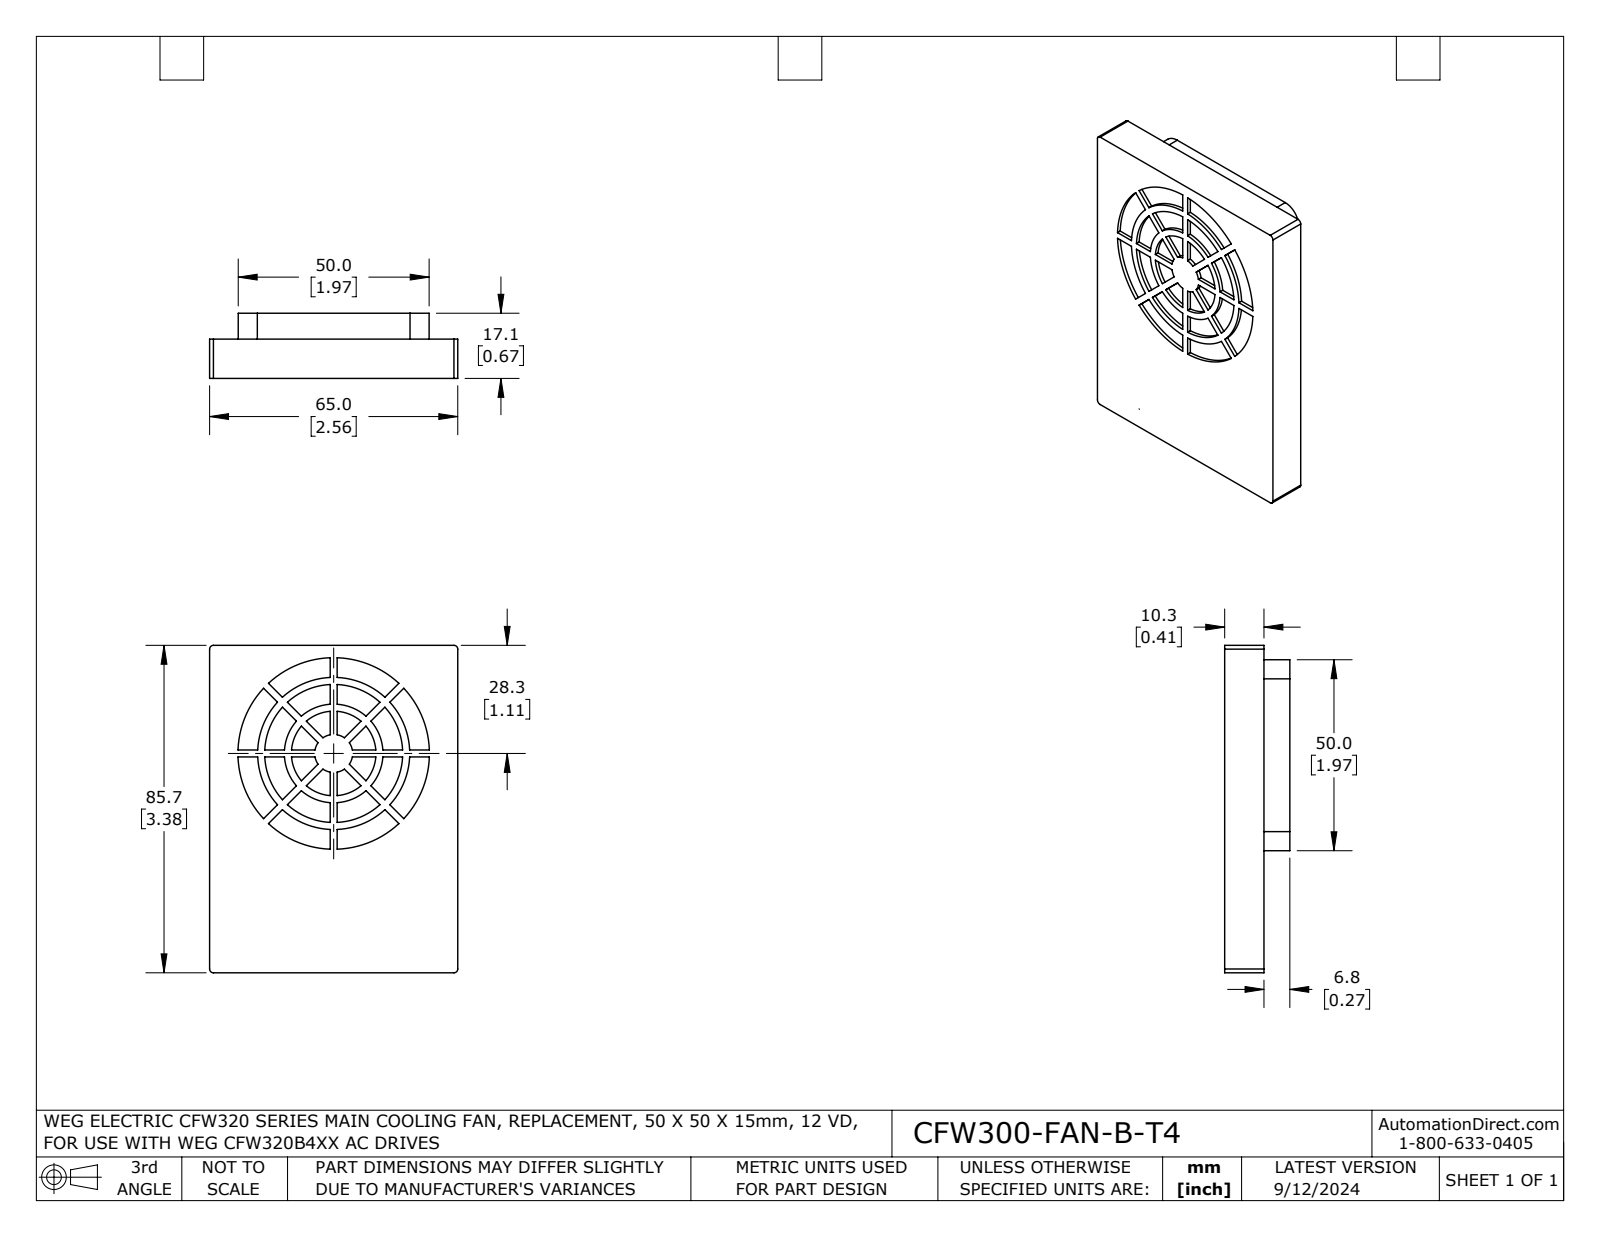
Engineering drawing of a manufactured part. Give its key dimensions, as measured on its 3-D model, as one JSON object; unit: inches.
{"part_name": "CFW300-FAN-B-T4", "step_written_by": "SolidWorks 2021 (AUTOMOTIVE_DESIGN)", "units": "inches", "bodies": {"solids": 1, "faces": 156, "planar": 92, "cylindrical": 64, "other": 0}, "overall_size": [3.375, 2.559, 0.672], "volume_in3": 4.372, "surface_area_in2": 25.66, "round_holes": [[1.424, 1], [1.89, 1], [1.975, 1]], "round_bosses_or_shafts": [[1.569, 1], [1.017, 1], [0.984, 1]], "partial_cylinders_radius": [[0.039, 4], [0.197, 4], [0.196, 1], [0.436, 1]], "face_to_face_distances": [0.405, 0.039, 0.633, 0.366, 0.267, 0.672, 0.228, 0.593, 2.559, 3.375], "hole_center_spacings": [0.018]}
